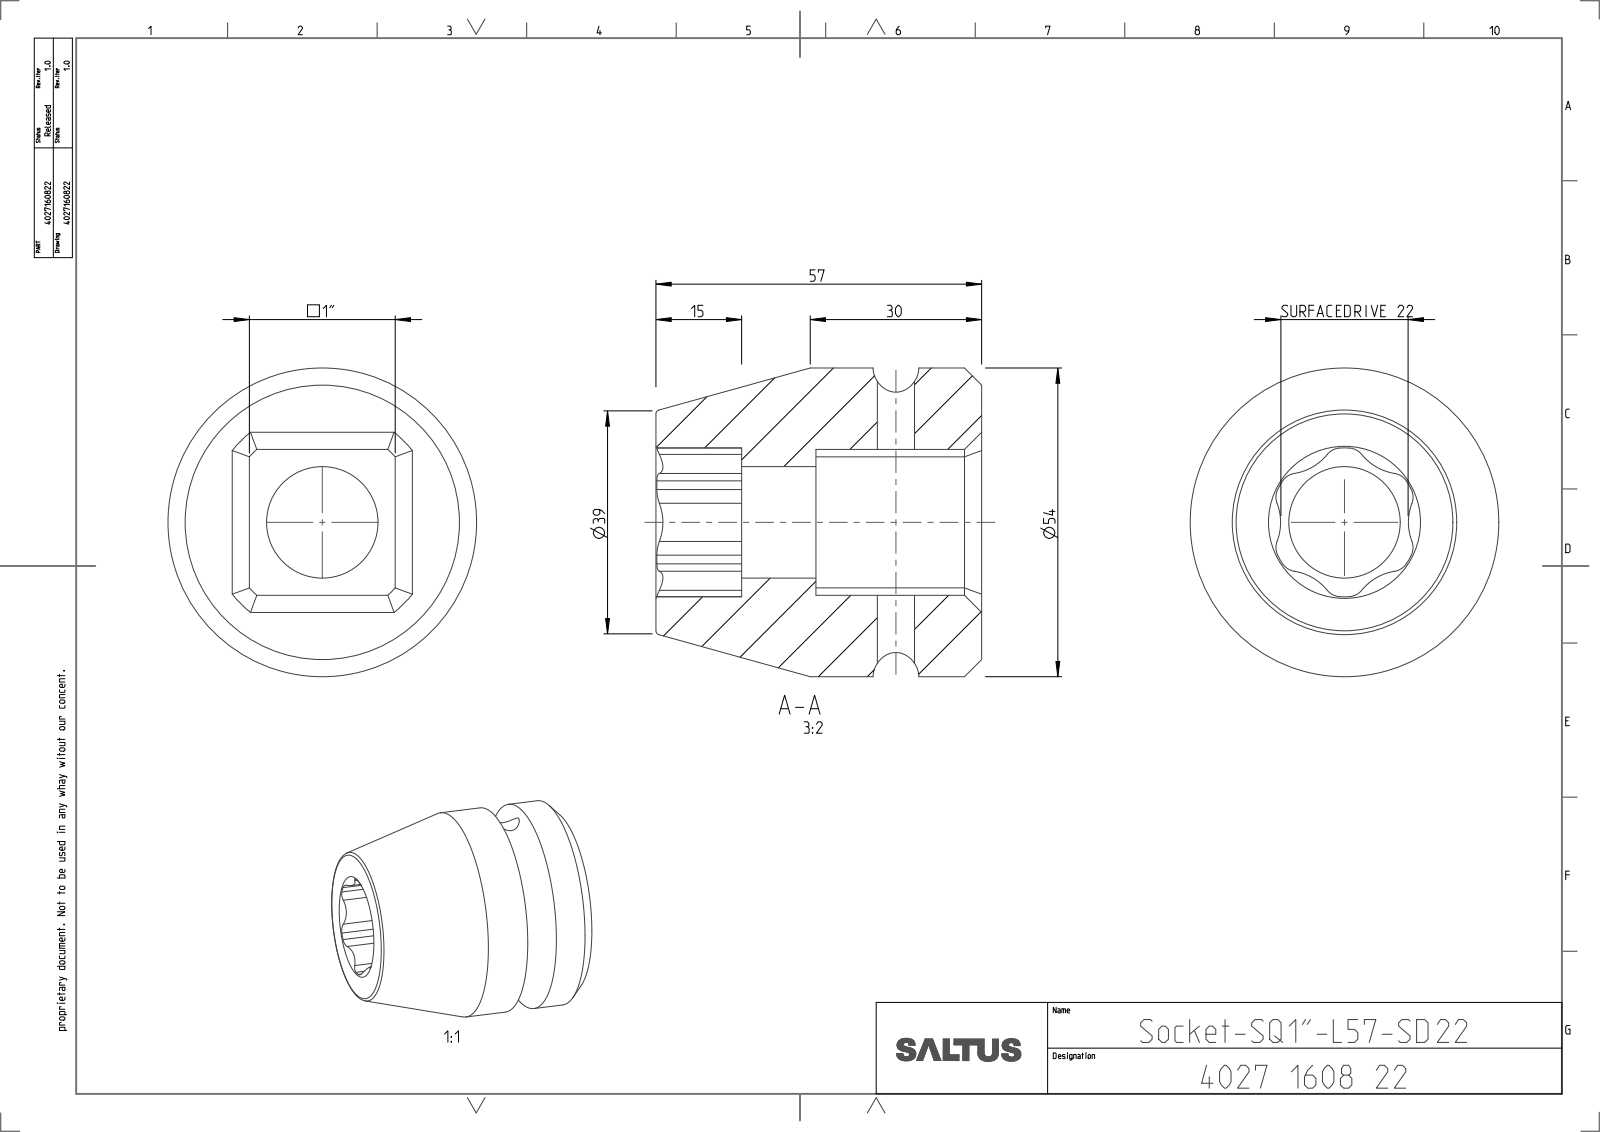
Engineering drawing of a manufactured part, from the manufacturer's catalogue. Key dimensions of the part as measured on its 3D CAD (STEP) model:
Part name (STEP PRODUCT): 4027160822
STEP written by: CREO PARAMETRIC BY PTC INC, 2022414 (CONFIG_CONTROL_DESIGN)
Units: millimetres
Bodies: 1 solid, 64 faces (12 planar, 38 cylindrical, 14 other)
Overall size (bounding box): 57 × 54 × 54
Volume: 79 351 mm³ · Surface area: 17 306 mm²
Round holes (diameter × count): ⌀6.5 ×1, ⌀19.5 ×1
Round bosses / shafts (diameter × count): ⌀54 ×1
Partial cylindrical surfaces — rounded edges, fillets, slot ends (radius × count): R3 ×12, R9.3 ×6, R13.03 ×1, R17.15 ×1
Main face-to-face distances: 25.52, 57, 29, 28, 42, 13, 15
